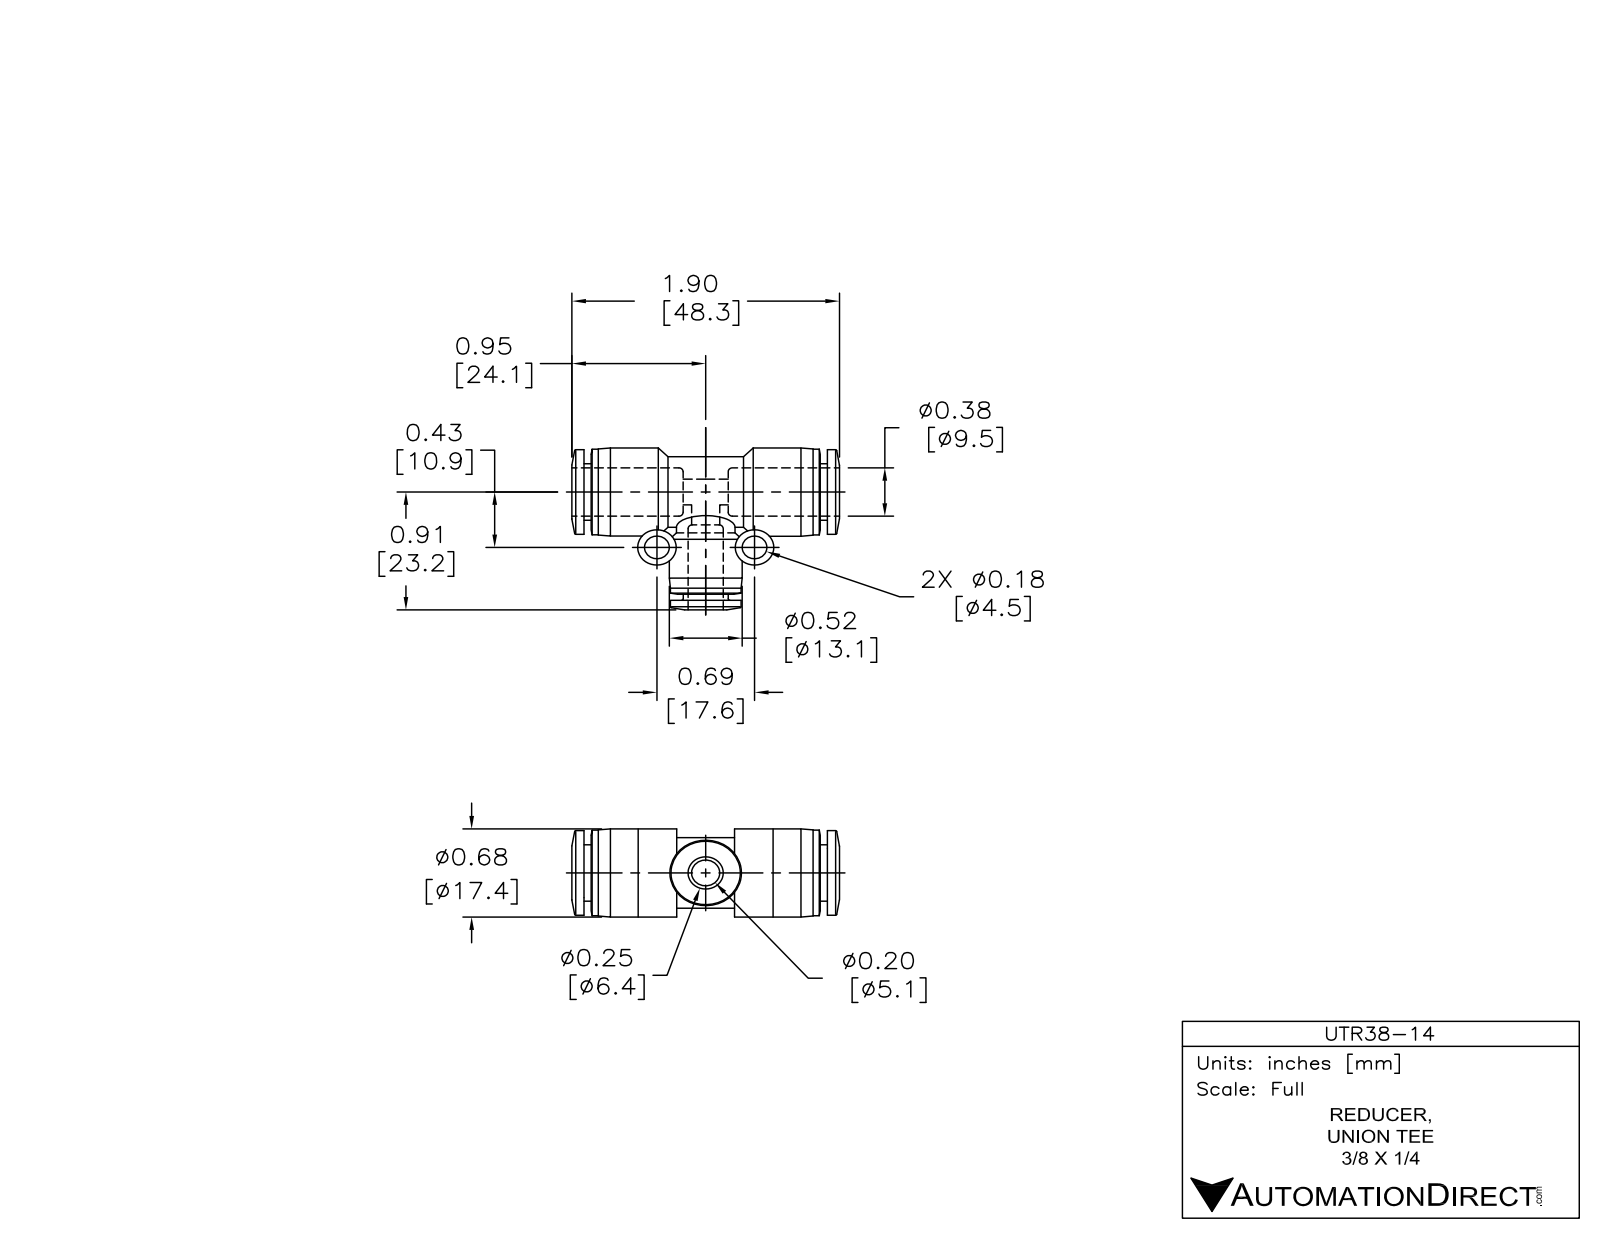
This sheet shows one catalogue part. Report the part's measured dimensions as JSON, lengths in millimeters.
{"part_name": "UTR38-14", "step_written_by": "SolidWorks 2015 (AUTOMOTIVE_DESIGN)", "units": "millimeters", "bodies": {"solids": 1, "faces": 105, "planar": 15, "cylindrical": 46, "other": 44}, "overall_size": [48.6, 32.2, 17.5], "volume_mm3": 8600, "surface_area_mm2": 7013, "round_holes": [[4.5, 2], [5, 2], [6.6, 1], [9.8, 1]], "round_bosses_or_shafts": [[7, 2], [17.5, 1], [17, 1], [16.8, 1], [14, 1], [13, 1], [12.6, 1], [11.2, 1]], "face_to_face_distances": [1.3, 42.9, 44.2, 17.9, 26.3, 16.6, 25, 41.6, 8.4, 17.5], "hole_center_spacings": [17.5]}
